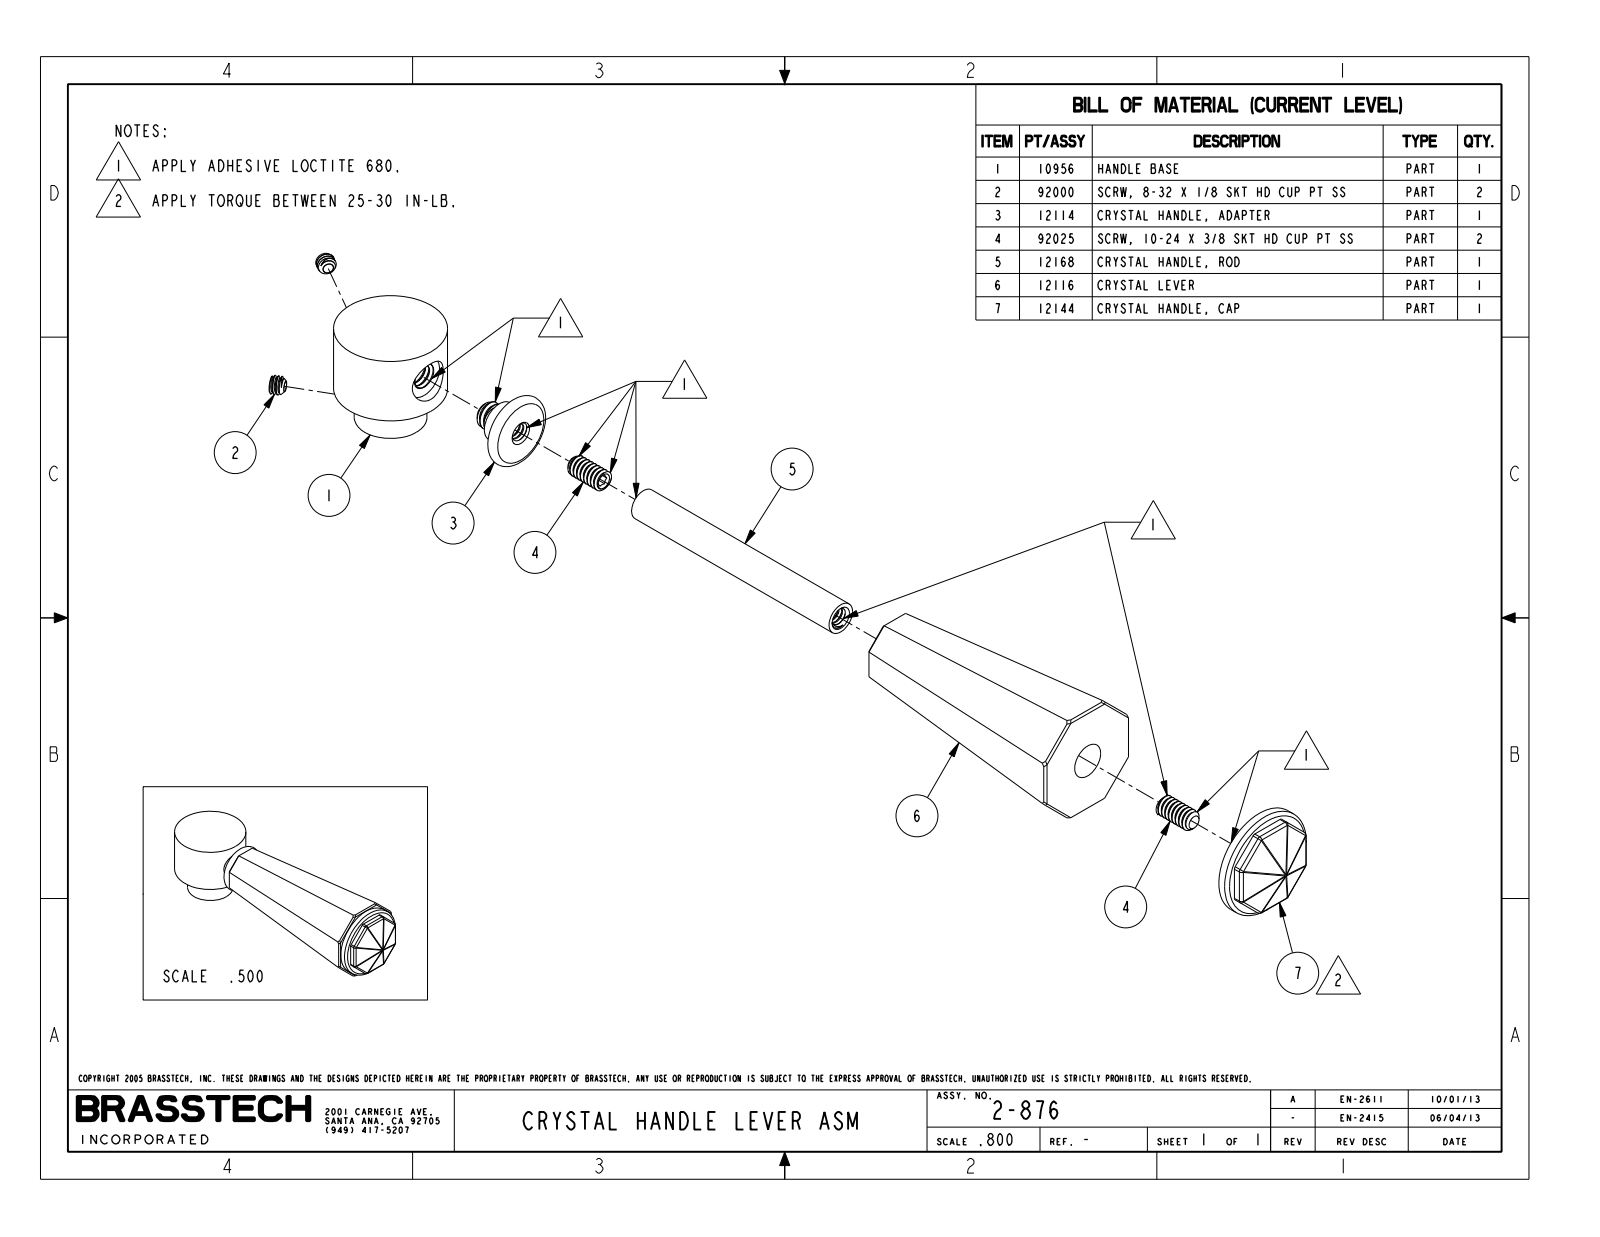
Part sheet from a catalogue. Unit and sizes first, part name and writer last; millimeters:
Units: millimetres
Overall size (bounding box): 97.7 × 28.9 × 26.1
Round holes (diameter × count): ⌀3.5 ×2, ⌀3.8 ×1, ⌀5.1 ×1, ⌀8 ×1, ⌀8.6 ×1, ⌀9.8 ×1
Round bosses / shafts (diameter × count): ⌀24.9 ×2, ⌀4.2 ×2, ⌀15.9 ×1, ⌀9.3 ×1, ⌀7.2 ×1, ⌀6.4 ×1, ⌀4.8 ×1, ⌀4.6 ×1
Partial cylindrical surfaces — rounded edges, fillets, slot ends (radius × count): R0.8 ×24, R4.7 ×1
Main face-to-face distances: 60, 2.5, 62.5, 6.6, 66.6, 69.1, 3.9, 7.9, 4.1, 65.1
Volume: 32 870 mm³ · Surface area: 18 490 mm²
Bodies: 9 solids, 647 faces (210 planar, 214 cylindrical, 223 other)
Part name (STEP PRODUCT): 10956; 92000; 12114; 92025 (+4 more)
STEP written by: CREO PARAMETRIC BY PTC INC, 2018400 (CONFIG_CONTROL_DESIGN)
